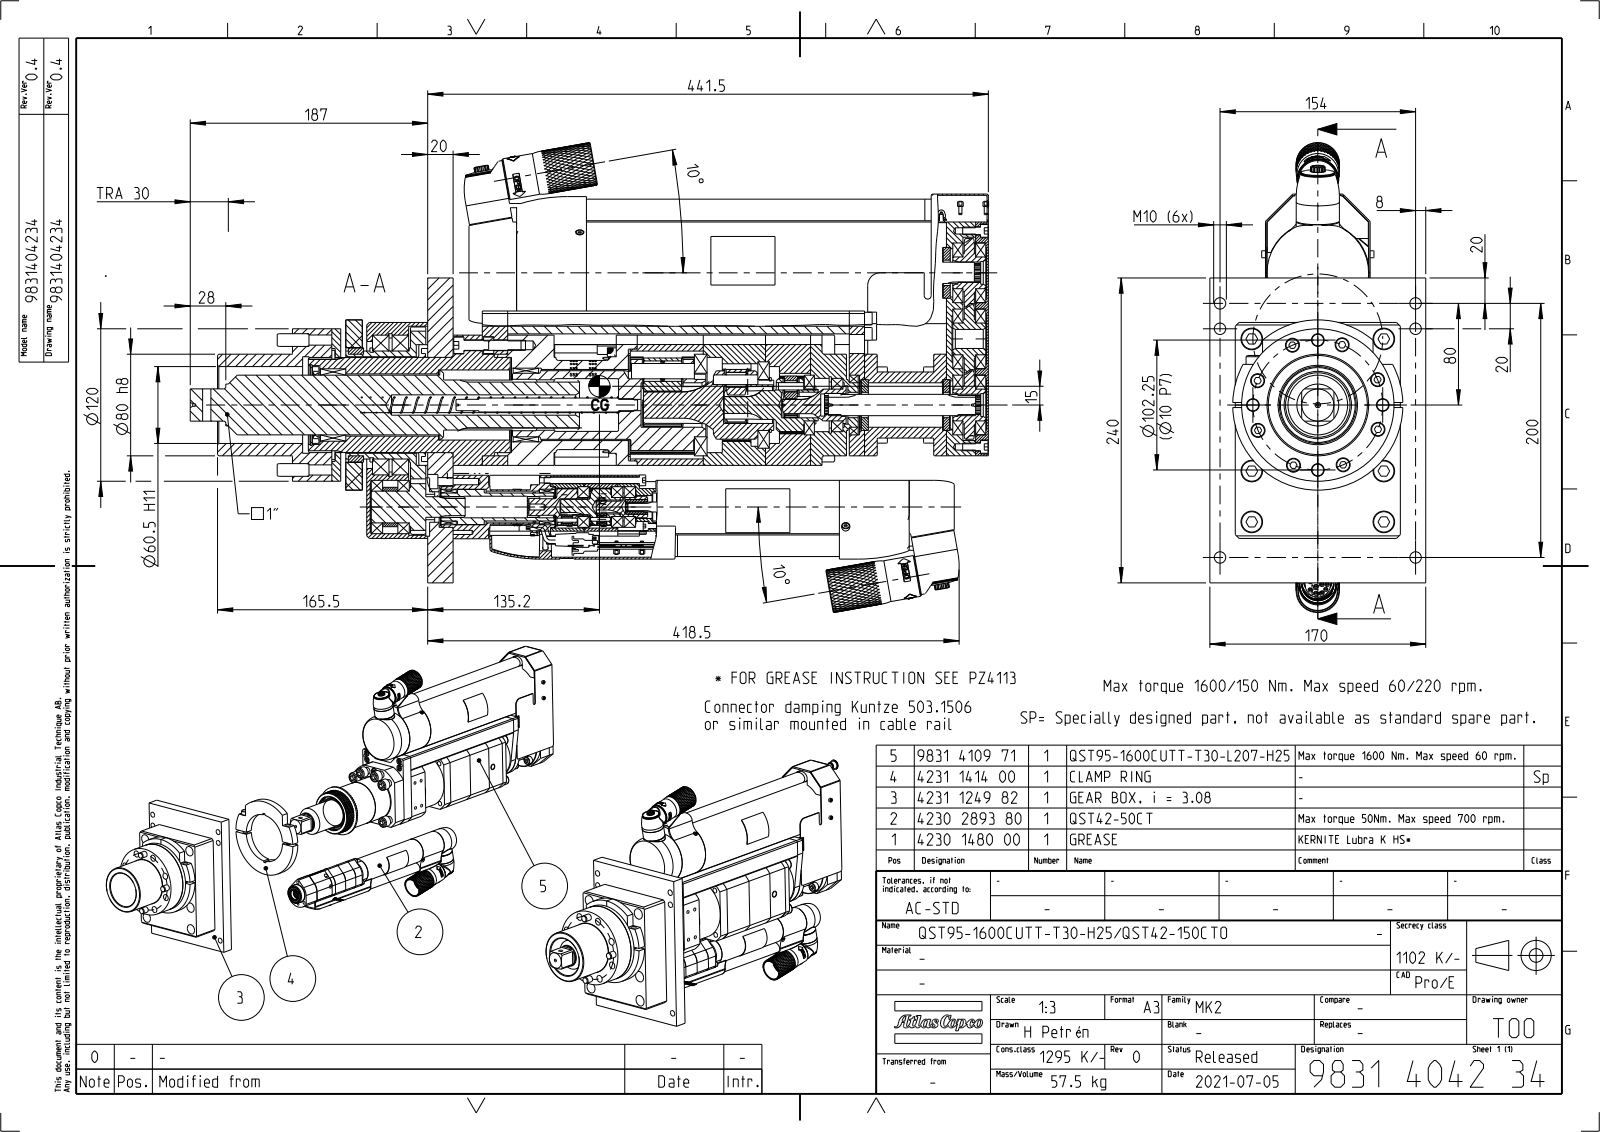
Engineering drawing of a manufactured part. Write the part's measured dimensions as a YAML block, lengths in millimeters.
part_name: "EXT_COMP_SW0009"
step_written_by: "CREO PARAMETRIC BY PTC INC, 2020281 (CONFIG_CONTROL_DESIGN)"
units: millimeters
bodies: {solids: 2, faces: 5030, planar: 2576, cylindrical: 843, other: 1611}
overall_size: [628.5, 369.9, 170]
volume: 9446000
surface_area: 820600
round_holes:
  - {diameter: 11, count: 14}
  - {diameter: 4.9, count: 8}
  - {diameter: 2.9, count: 6}
  - {diameter: 4, count: 6}
  - {diameter: 7.9, count: 6}
  - {diameter: 9, count: 6}
  - {diameter: 17, count: 6}
  - {diameter: 3.3, count: 4}
  - {diameter: 6.3, count: 4}
  - {diameter: 6.9, count: 4}
  - {diameter: 10.5, count: 4}
  - {diameter: 3.5, count: 3}
round_bosses_or_shafts:
  - {diameter: 10, count: 22}
  - {diameter: 16, count: 12}
  - {diameter: 34, count: 7}
  - {diameter: 3, count: 4}
  - {diameter: 8.5, count: 3}
  - {diameter: 80, count: 2}
  - {diameter: 32.6, count: 2}
  - {diameter: 32.5, count: 2}
partial_cylinders:
  - {radius: 16, count: 58}
  - {radius: 0.5, count: 14}
  - {radius: 1, count: 7}
  - {radius: 1.5, count: 6}
  - {radius: 0.2, count: 4}
  - {radius: 0.8, count: 4}
  - {radius: 40, count: 4}
  - {radius: 6.5, count: 3}
face_to_face_distances: [1, 20, 95, 7.3, 87.7, 6.3, 88.7, 81.4, 112.5, 109.5]
hole_center_spacings: [39.1, 72.3, 90.1, 12, 57.7, 104, 8.6, 19.7]
